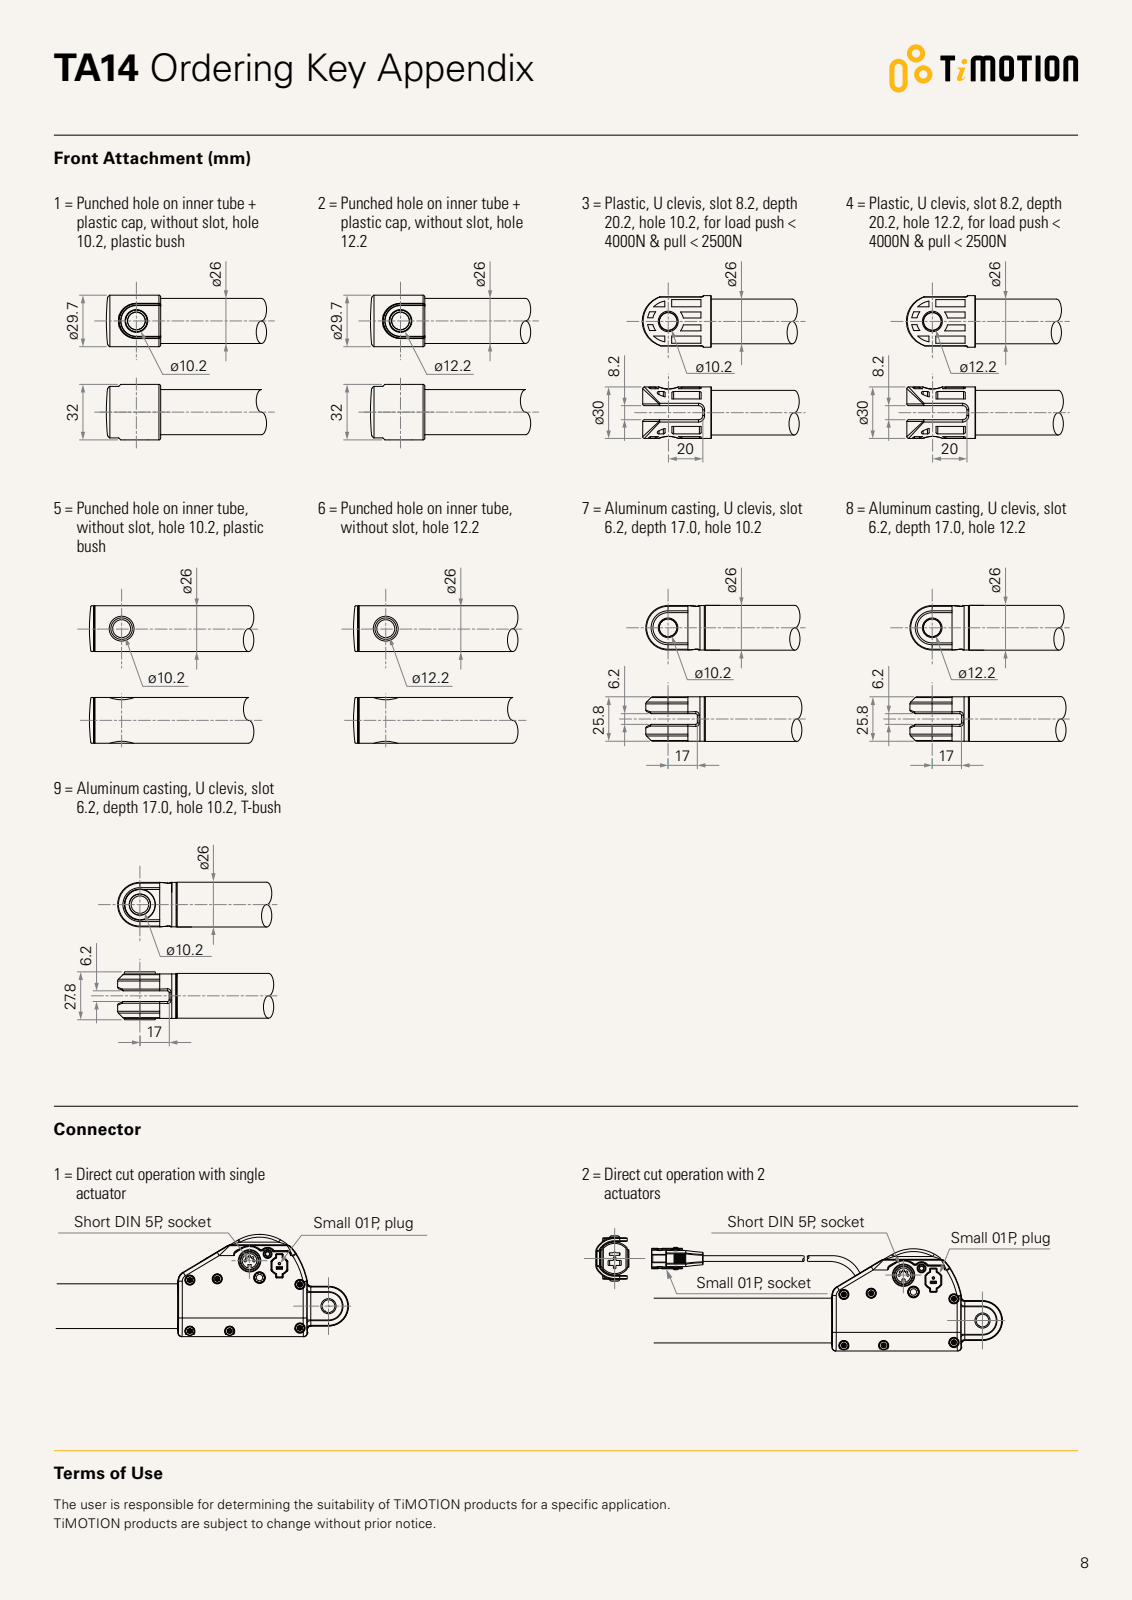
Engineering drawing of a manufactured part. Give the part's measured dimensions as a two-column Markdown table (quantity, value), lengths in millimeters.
| quantity | value |
| --- | --- |
| STEP written by | SolidWorks 2010 (AUTOMOTIVE_DESIGN) |
| units | millimeters |
| bodies | 0 solids, 705 faces (191 planar, 181 cylindrical, 333 other) |
| overall size | 397 × 166.96 × 82.27 |
| round holes (diameter × count) | 7.5 × 4, 10.2 × 2, 4.6 × 1, 8.8 × 1, 12.2 × 1, 12.5 × 1, 17 × 1, 26.1 × 1 |
| round bosses / shafts (diameter × count) | 7.3 × 3, 29.7 × 1, 26 × 1 |
| partial cylindrical surfaces (radius × count) | 1 × 37, 3 × 32, 0.5 × 18, 0.3 × 8, 4 × 4, 8 × 3, 10 × 3, 3.75 × 2 |
| main face-to-face distances | 57, 6, 63, 2, 11.05, 14.55, 80.6, 74.6, 17.6, 104 |
| hole center spacings | 28.9, 341.15, 15.69, 22.02, 29.77, 32.96, 34.01, 35 |
